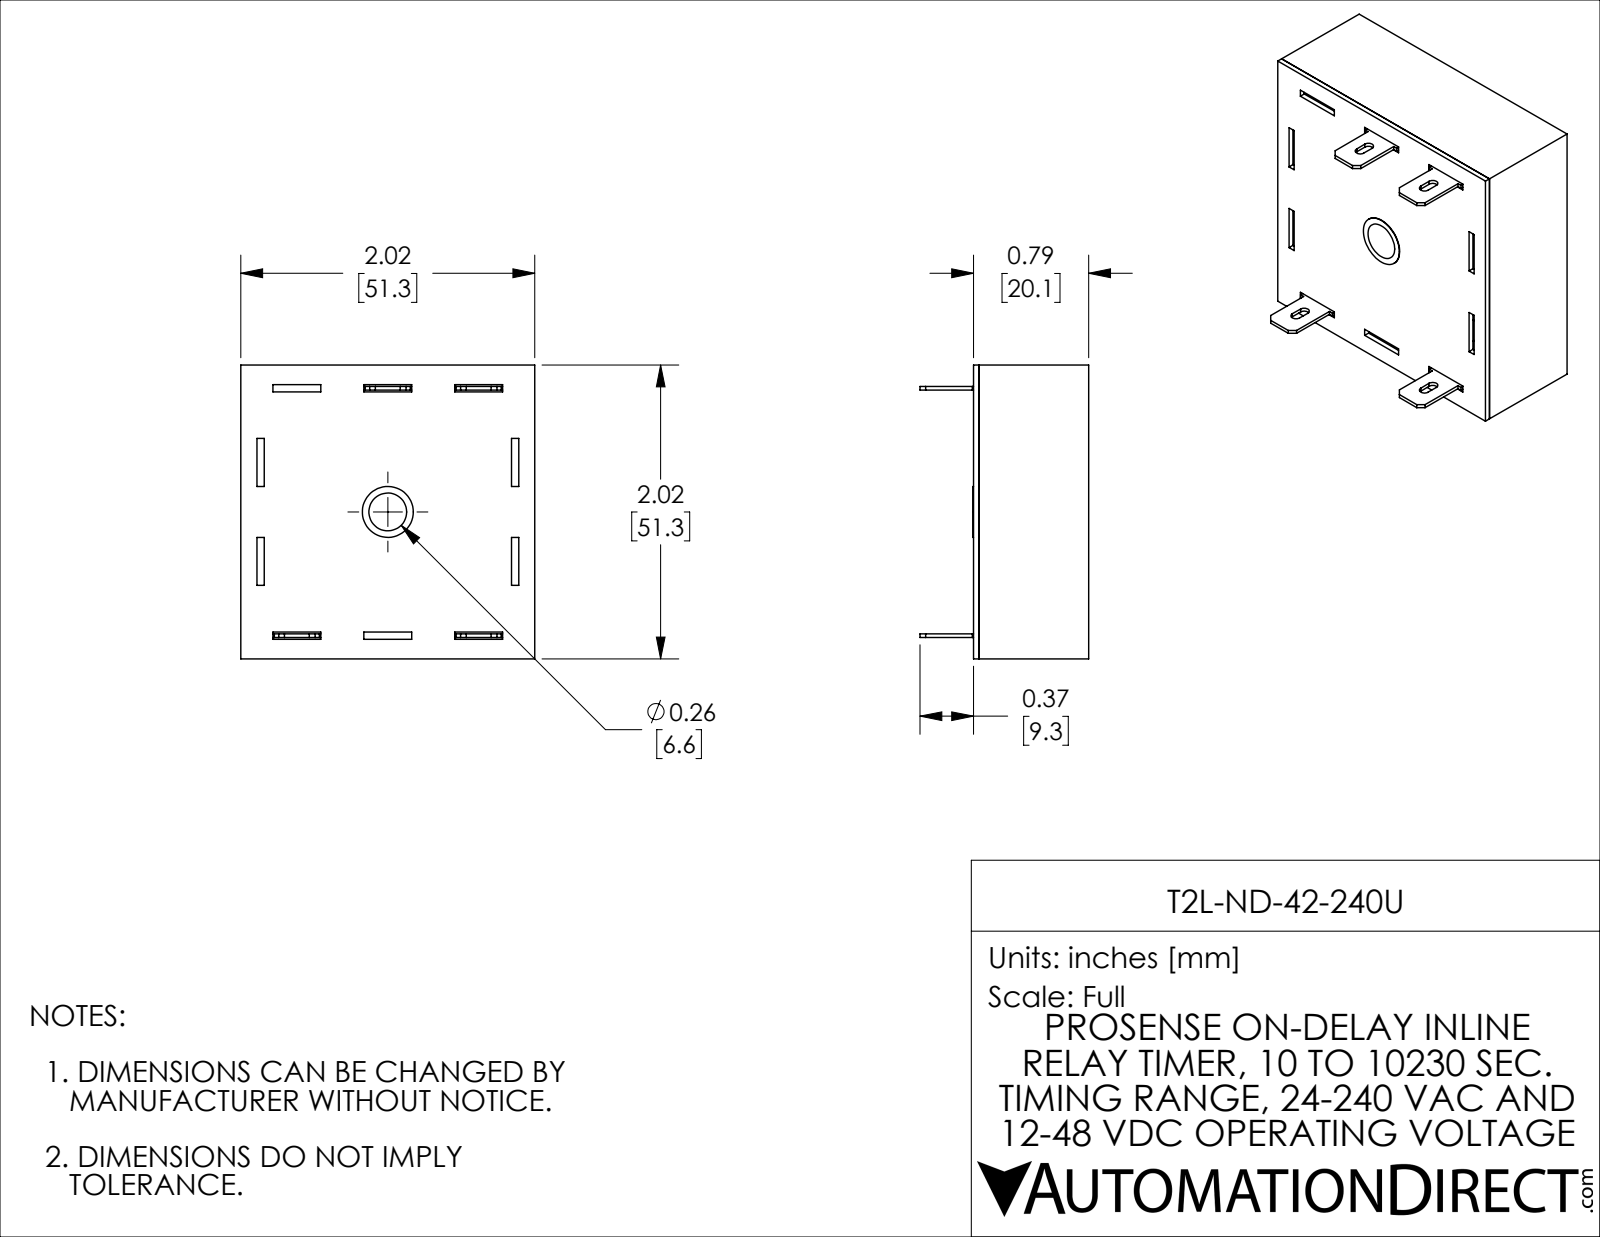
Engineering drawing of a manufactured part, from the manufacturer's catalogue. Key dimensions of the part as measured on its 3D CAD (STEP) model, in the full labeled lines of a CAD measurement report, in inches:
Part name (STEP PRODUCT): T2L-ND-42-240U
STEP written by: SolidWorks 2021 (CONFIG_CONTROL_DESIGN)
Units: inches
Bodies: 6 solids, 160 faces (146 planar, 12 cylindrical, 2 other)
Overall size (bounding box): 2.02 × 2.02 × 1.16
Volume: 0.641 in³ · Surface area: 32.38 in²
Round holes (diameter × count): ⌀0.35 ×1
Partial cylindrical surfaces — rounded edges, fillets, slot ends (radius × count): R0.035 ×6
Main face-to-face distances: 0.045, 1.975, 0.754, 0.792, 0.038, 0.709, 0.747, 2.02, 1.93, 1.7
